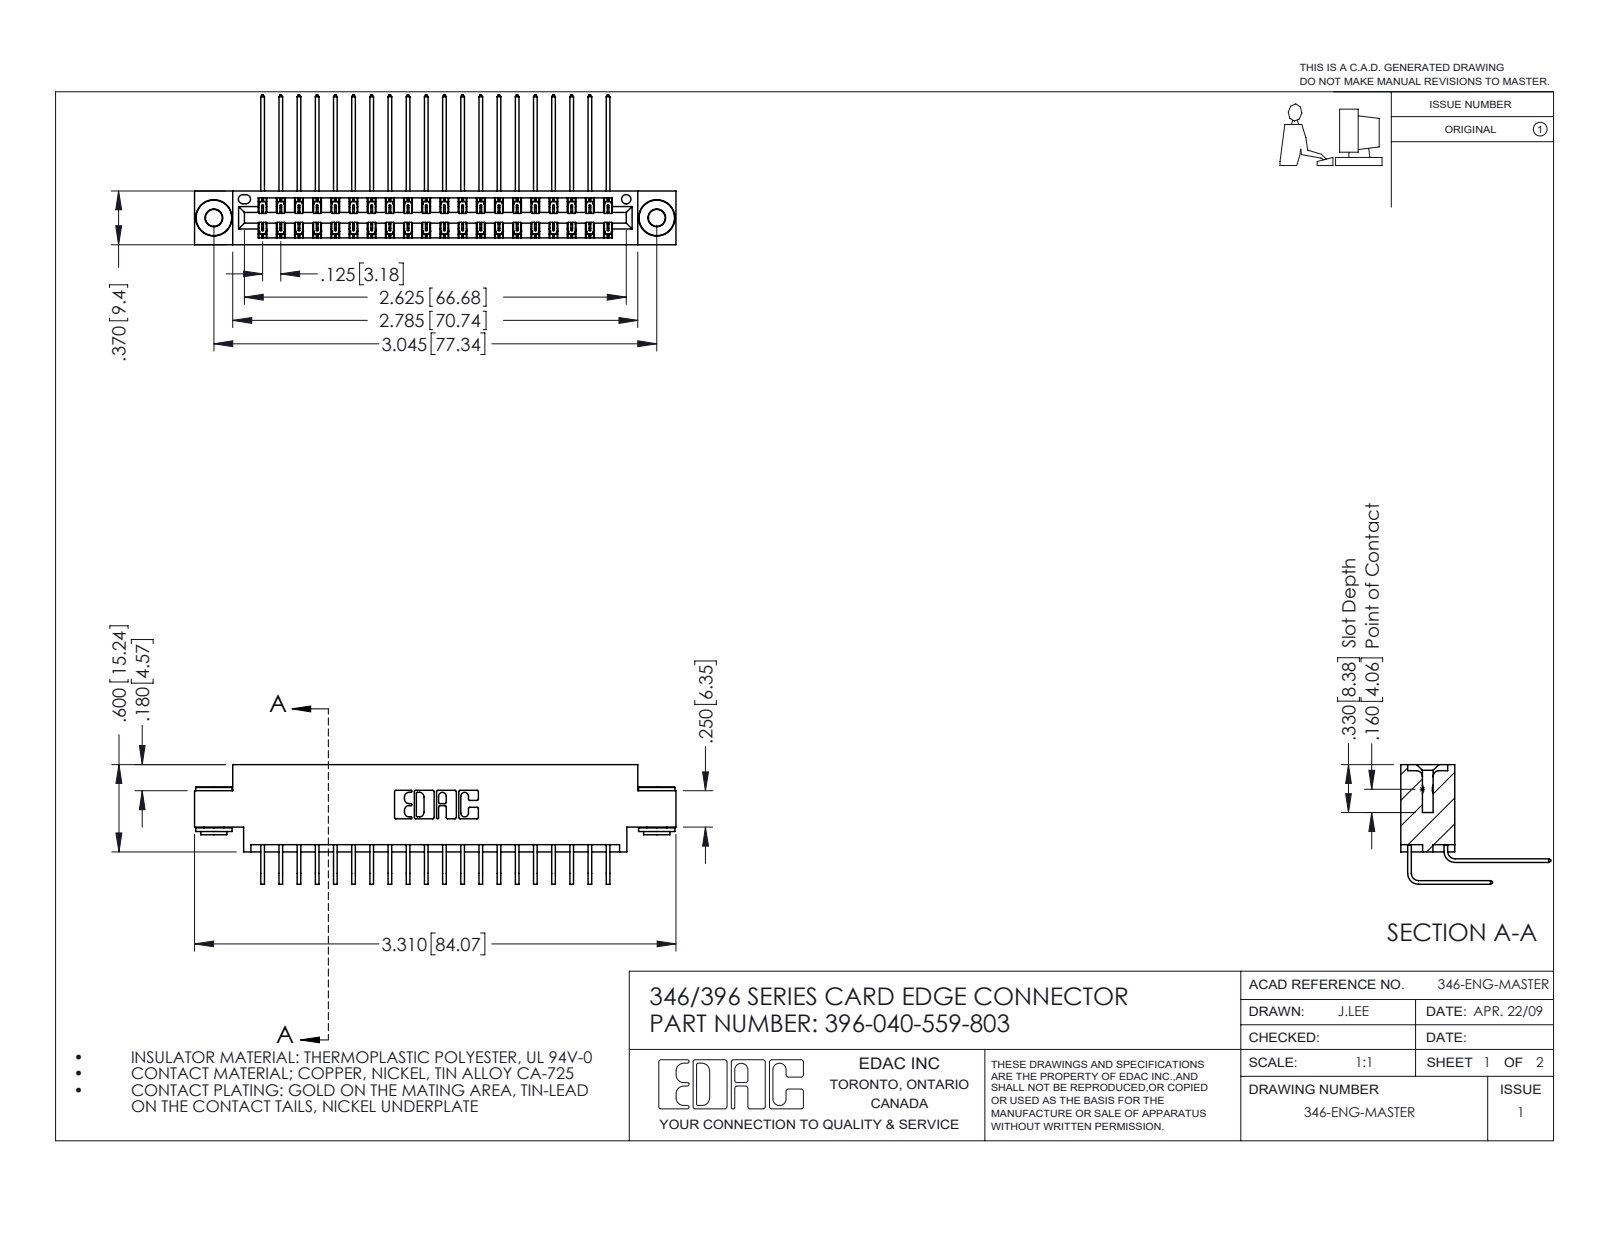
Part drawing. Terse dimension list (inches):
name: 345-292-001_559 Tail - 2; 345-292-001_558 559 Tail - 1; 396-040-559-803; 345-250-002_345-250-002-102 (+1 more)
written by: SolidWorks 2016 (CONFIG_CONTROL_DESIGN)
unit: in
bodies: 43 solids, 2324 faces (1570 planar, 746 cylindrical, 8 other)
size: 3.31 × 1.03 × 0.823
volume: 0.496 in³; area: 19.1 in²
holes: 2× ⌀0.116, 2× ⌀0.156, 1× ⌀0.064
bosses: 2× ⌀0.25, 2× ⌀0.18, 2× ⌀0.136
rounds: 60× R0.006, 22× R0.01, 6× R0.007, 6× R0.031, 3× R0.026, 2× R0.014, 2× R0.022, 2× R0.024
face distances: 0.048, 0.322, 0.37, 0.025, 0.25, 0.072, 0.298, 0.275, 0.15, 0.148
hole spacings: 0.246, 2.837, 3.045
